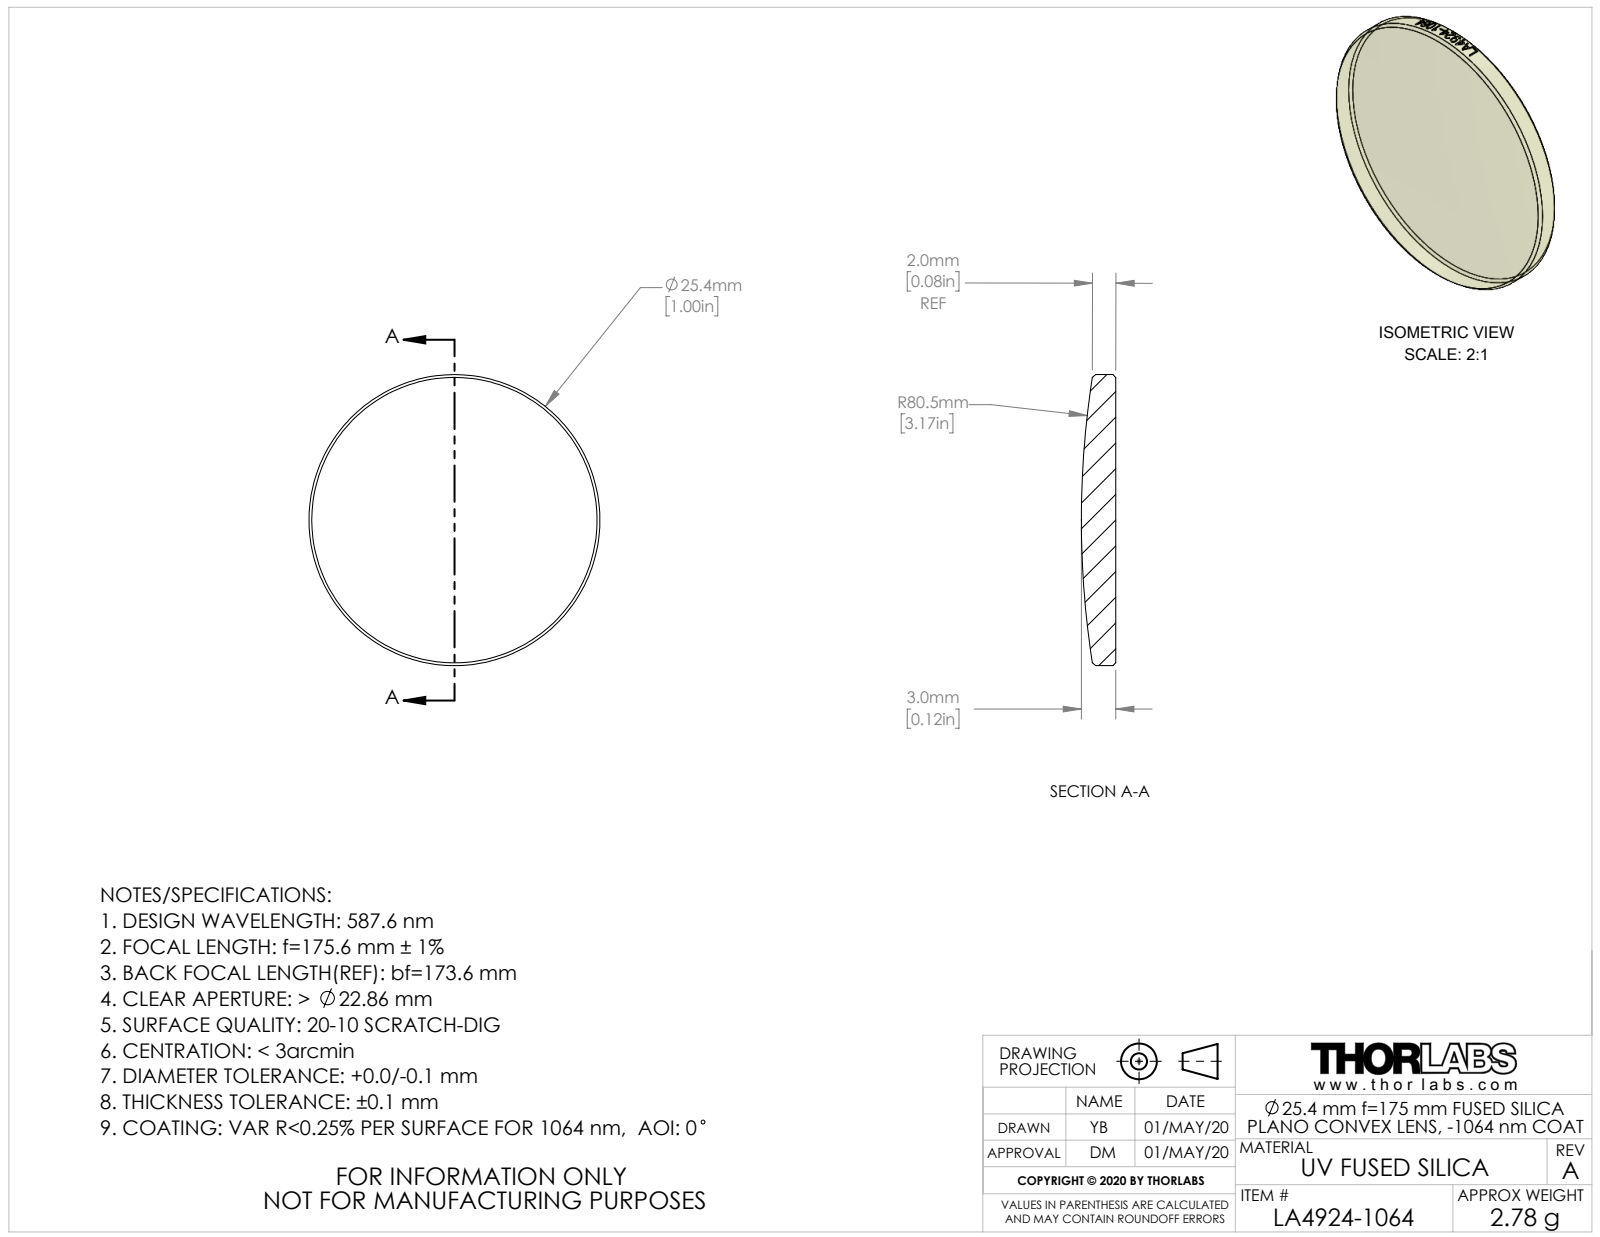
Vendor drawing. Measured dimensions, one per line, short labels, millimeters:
name: CTN015544-E0W
written by: SolidWorks 2018 (AUTOMOTIVE_DESIGN)
unit: mm
bodies: 1 solid, 29 faces (1 planar, 22 cylindrical, 6 other)
size: 25.4 × 25.4 × 3
volume: 1 263 mm³; area: 1 155 mm²
bosses: 1× ⌀25.4
